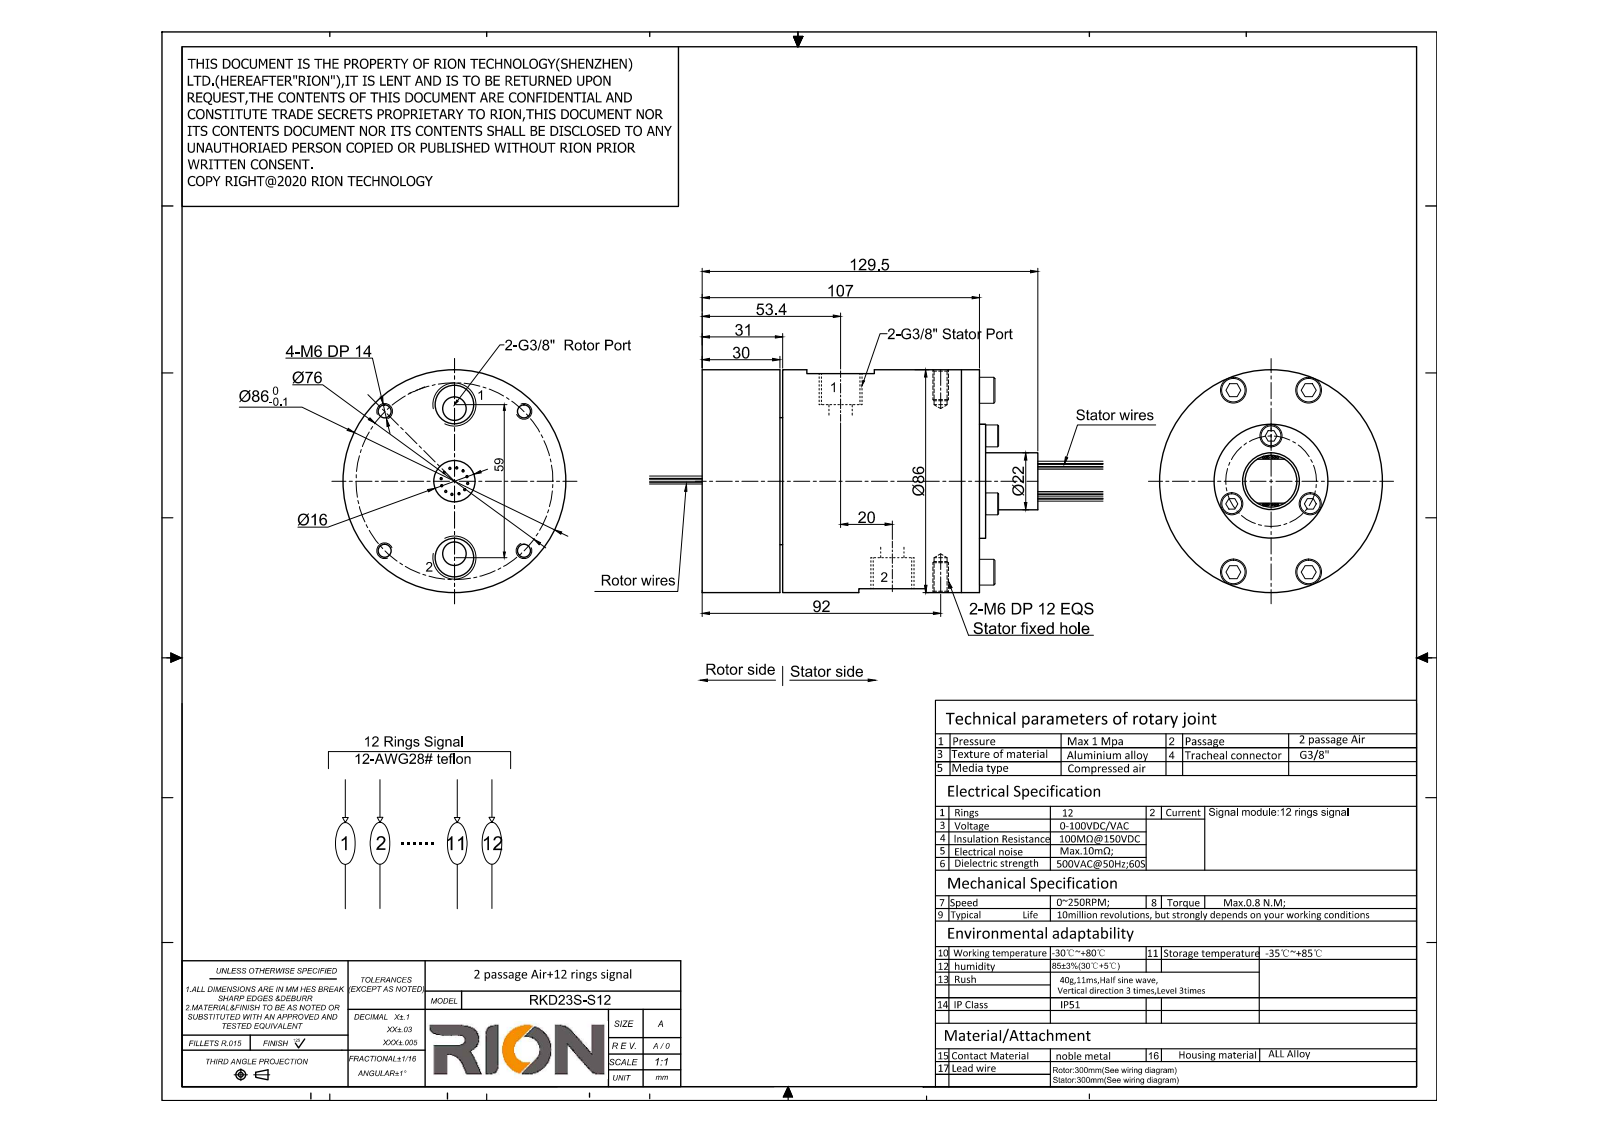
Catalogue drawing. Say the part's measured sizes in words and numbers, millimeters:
The part is named "MKD23S-S12". Its 3-D file was written by "SolidWorks 2014 (CONFIG_CONTROL_DESIGN)". It is 1 solid with 247 faces: 105 planar, 108 cylindrical and 34 other. Overall it measures 169.2 by 86 by 86 millimeters. Its volume is 619 153 cubic millimeters and its surface area 56 963 square millimeters. Round holes: 5 of diameter 5, 4 of diameter 9, 4 of diameter 15.25, 1 of diameter 4, 1 of diameter 16, 1 of diameter 20. Round bosses or shafts: 24 of diameter 0.8, 4 of diameter 10, 3 of diameter 8.5, 1 of diameter 86, 1 of diameter 49, 1 of diameter 44, 1 of diameter 22, 1 of diameter 19.9. The main face-to-face distances are 107, 1, 30, 31, 77, 76, 79.4, 109.4, 78.4, 2.4. The hole center spacings are 26.89, 27, 38, 53.74, 61.1, 62.45, 1.5, 28.
